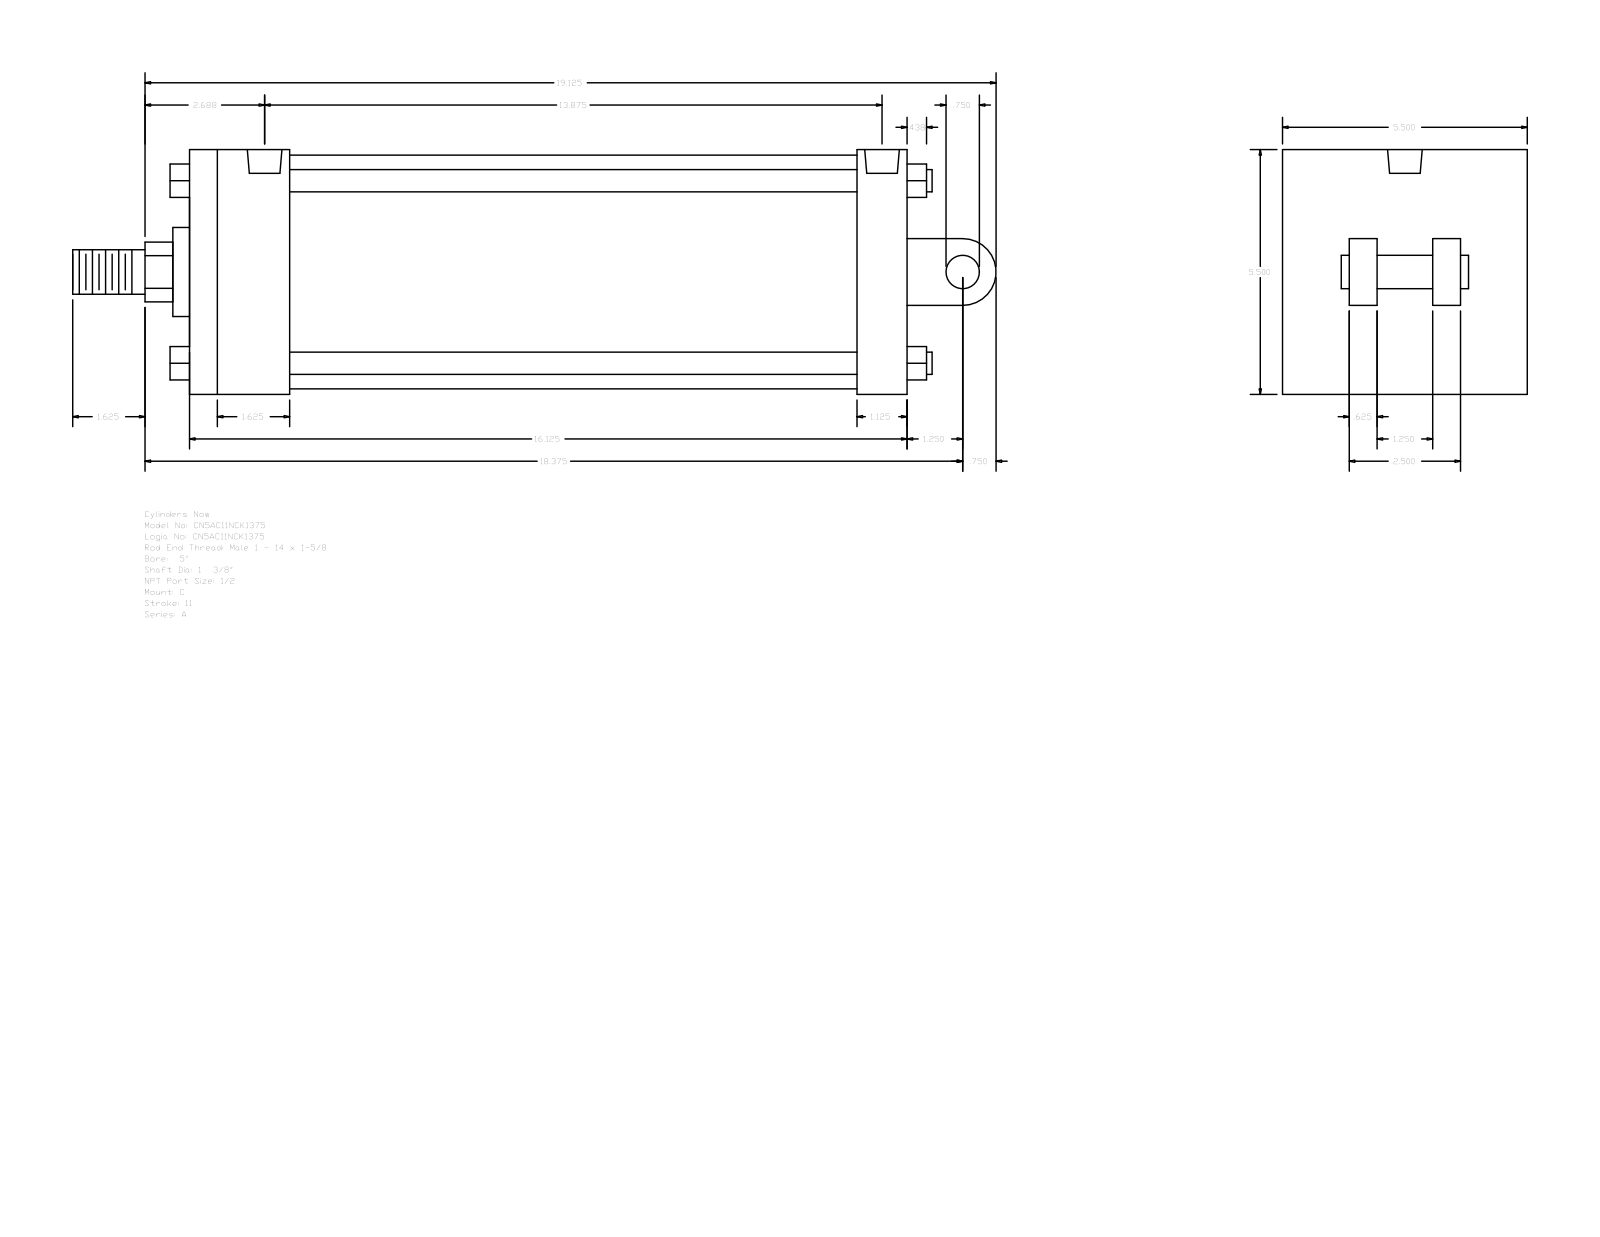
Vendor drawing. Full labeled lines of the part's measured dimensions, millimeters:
Part name (STEP PRODUCT): A_C__0500_1.375
STEP written by: GSSL Pune (CONFIG_CONTROL_DESIGN)
Units: millimetres
Bodies: 0 solids, 135 faces (102 planar, 33 cylindrical, 0 other)
Overall size (bounding box): 527.05 × 139.7 × 139.7
Round holes (diameter × count): ⌀8.73 ×4, ⌀19.77 ×2
Round bosses / shafts (diameter × count): ⌀12.7 ×4, ⌀133.35 ×1, ⌀50.8 ×1, ⌀34.92 ×1, ⌀25.4 ×1, ⌀19.05 ×1
Partial cylindrical surfaces — rounded edges, fillets, slot ends (radius × count): R17.06 ×1, R19.05 ×1
Main face-to-face distances: 139.7, 409.58, 57.15, 28.58, 381, 323.85, 352.43, 38.1, 53.97, 101.6
Hole centre spacings: 2.39, 347.65, 350.04, 352.43
